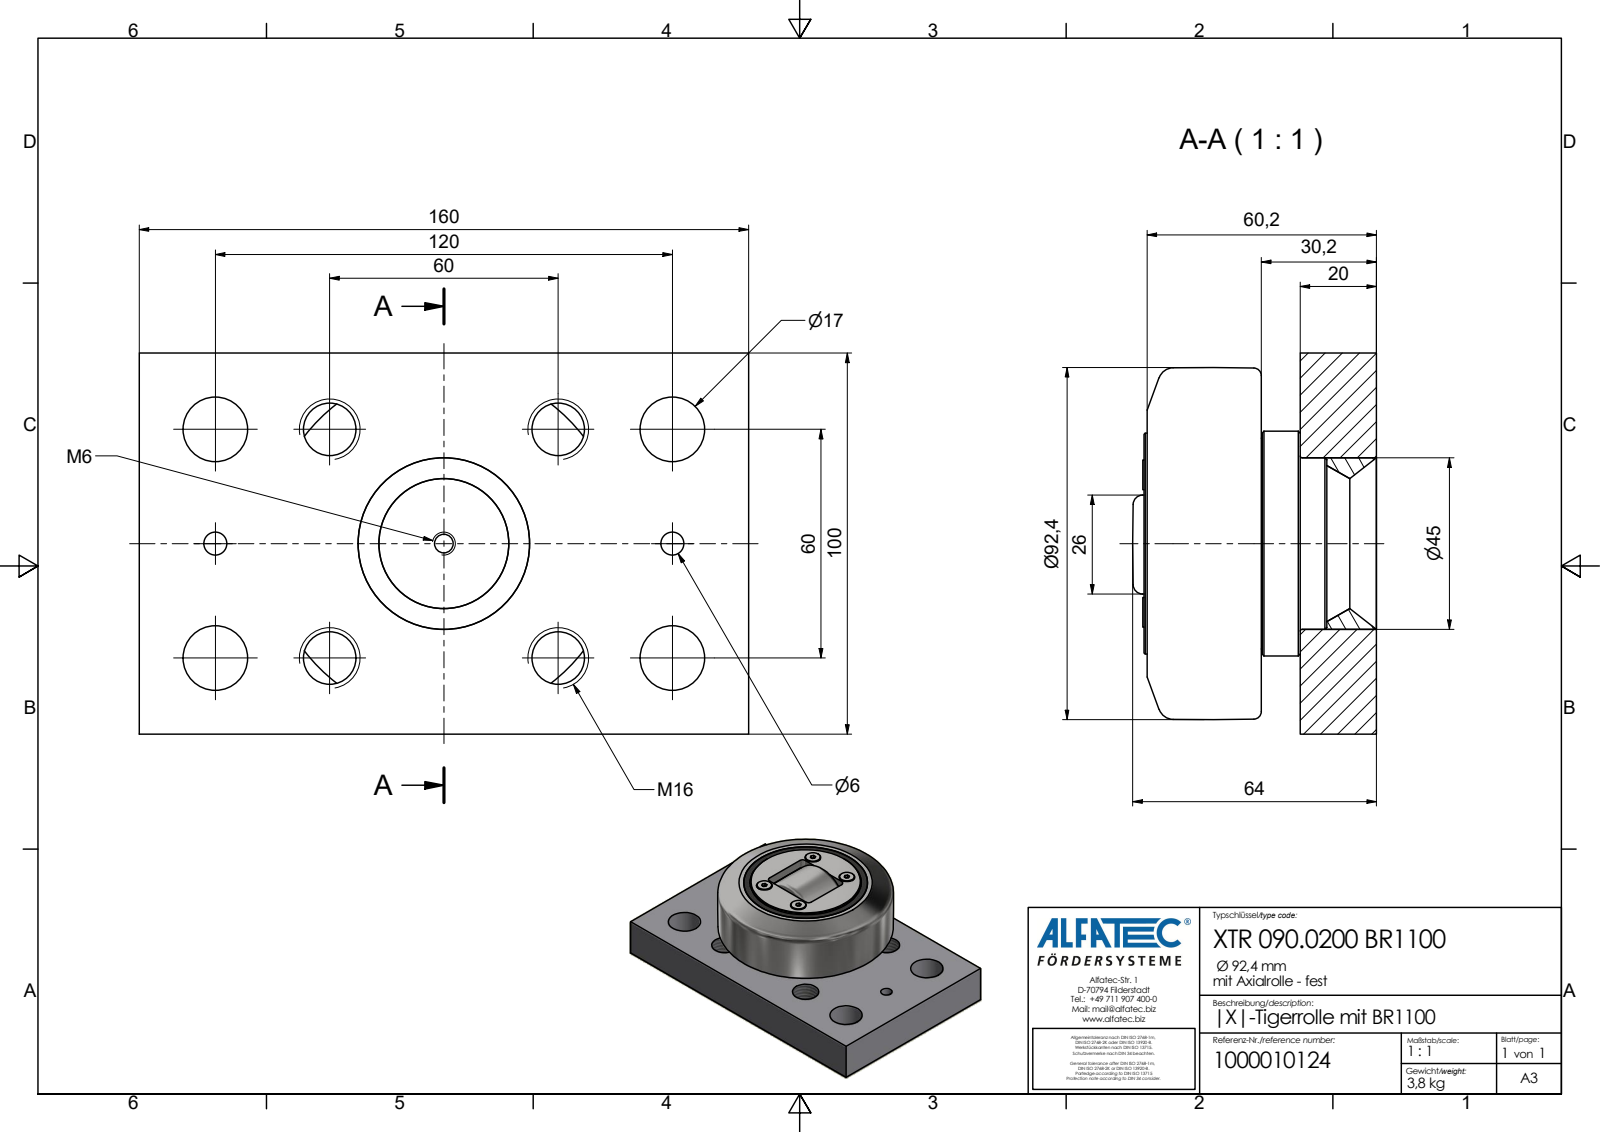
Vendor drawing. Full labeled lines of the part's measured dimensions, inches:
Part name (STEP PRODUCT): XTR 090.0200 BR1100_Kontur
STEP written by: Autodesk Inventor 2020 (AP242_MANAGED_MODEL_BASED_3D_ENGINEERING_MIM_LF)
Units: inches
Bodies: 1 solid, 93 faces (53 planar, 25 cylindrical, 15 other)
Overall size (bounding box): 6.299 × 3.937 × 2.52
Volume: 30.79 in³ · Surface area: 103.4 in²
Round holes (diameter × count): ⌀0.545 ×4, ⌀0.669 ×4, ⌀0.236 ×2, ⌀0.098 ×1, ⌀0.194 ×1
Round bosses / shafts (diameter × count): ⌀0.307 ×4, ⌀2.323 ×1, ⌀2.283 ×1, ⌀2.177 ×1
Partial cylindrical surfaces — rounded edges, fillets, slot ends (radius × count): R0.079 ×4, R0.059 ×1, R0.984 ×1
Main face-to-face distances: 0.787, 1.189, 0.402, 3.937, 6.299, 1.181, 2.402, 1.614, 1.213, 2.37
Hole centre spacings: 1.181, 1.67, 2.362, 2.641, 3.543, 3.735, 4.259, 4.87
